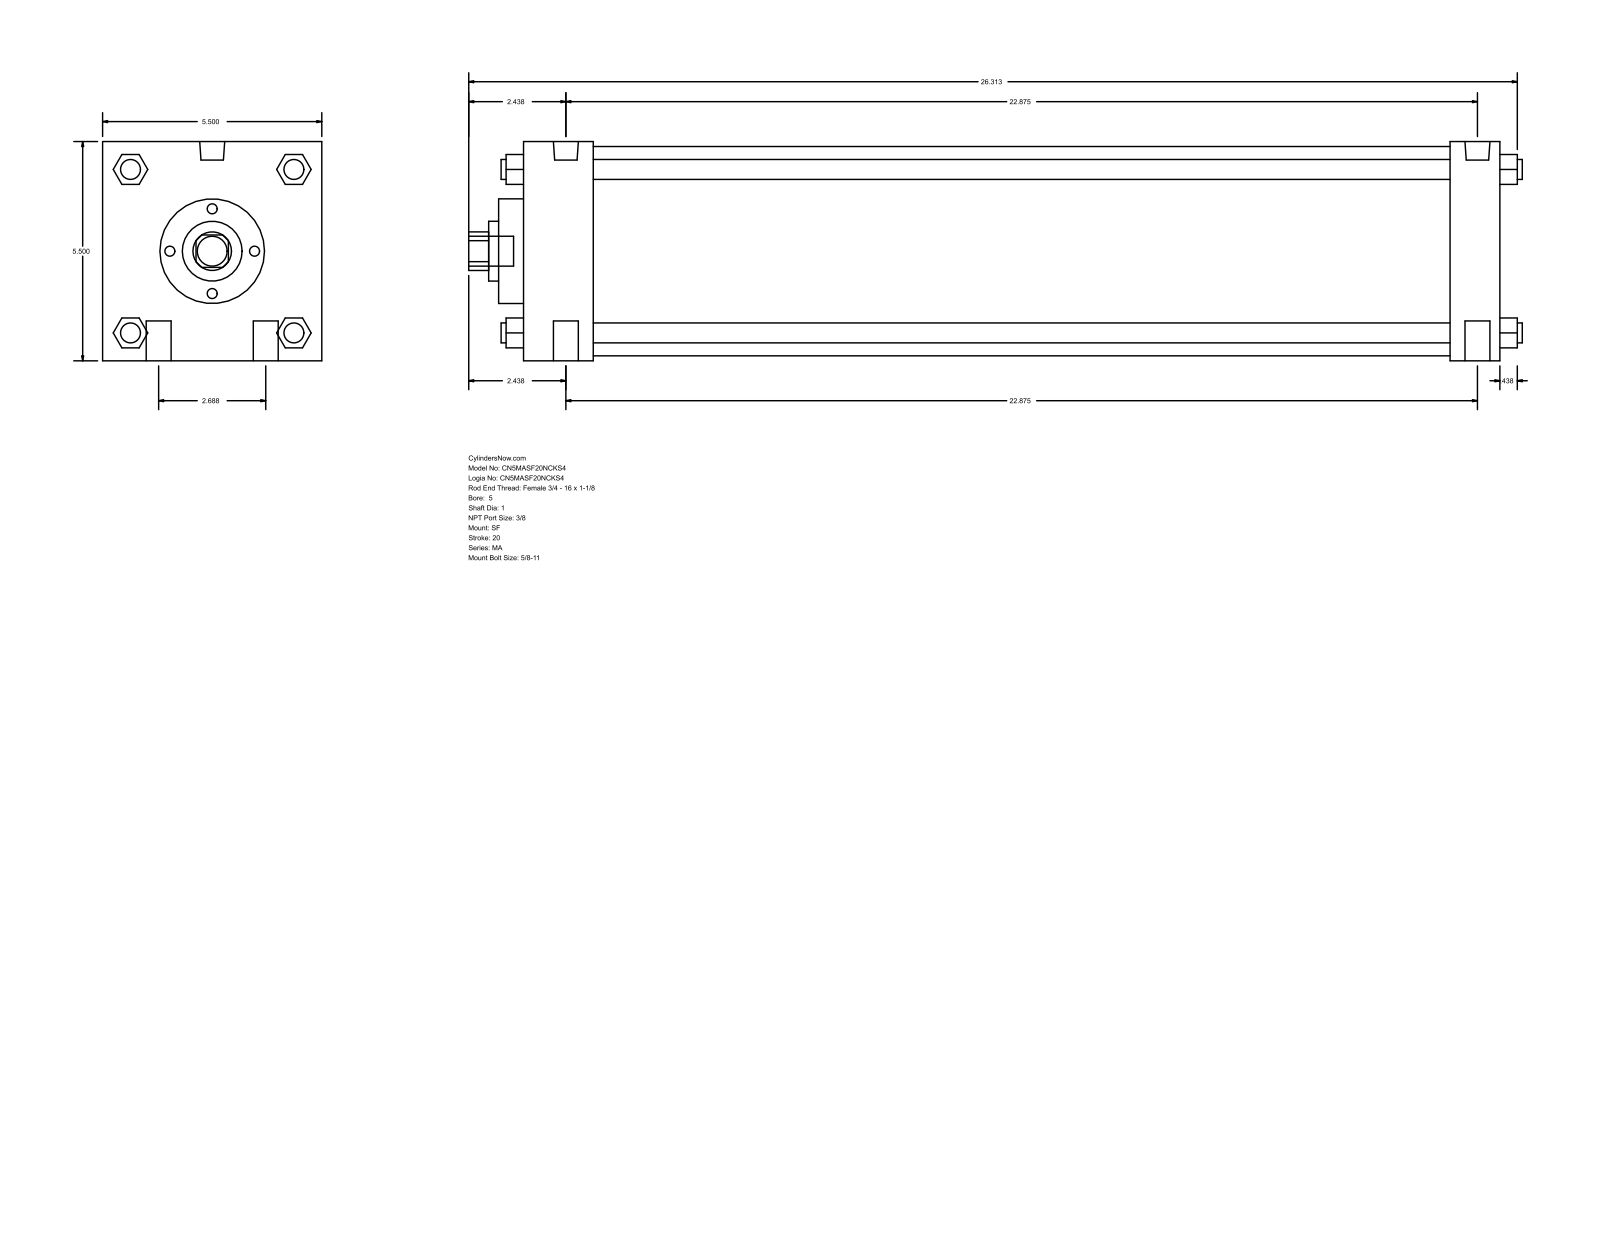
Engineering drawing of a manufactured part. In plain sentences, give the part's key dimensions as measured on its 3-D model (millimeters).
The part is named "MA_SF__0500_1". Its 3-D file was written by "GSSL Pune (CONFIG_CONTROL_DESIGN)". It is 0 solids with 126 faces: 95 planar, 31 cylindrical and 0 other. Overall it measures 671.51 by 139.7 by 139.7 millimeters. Round holes: 1 of diameter 25.4, 1 of diameter 38.1, 1 of diameter 66.67, 1 of diameter 133.35. Round bosses or shafts: 4 of diameter 15.88, 4 of diameter 12.7, 2 of diameter 15.93, 2 of diameter 11.11, 1 of diameter 19.05. Partial cylindrical surfaces (rounded edges, fillets, slot ends): 1 of radius 12.29. The main face-to-face distances are 139.7, 622.31, 44.46, 590.56, 546.1, 577.85, 31.75, 15.87, 60.33, 606.43.
